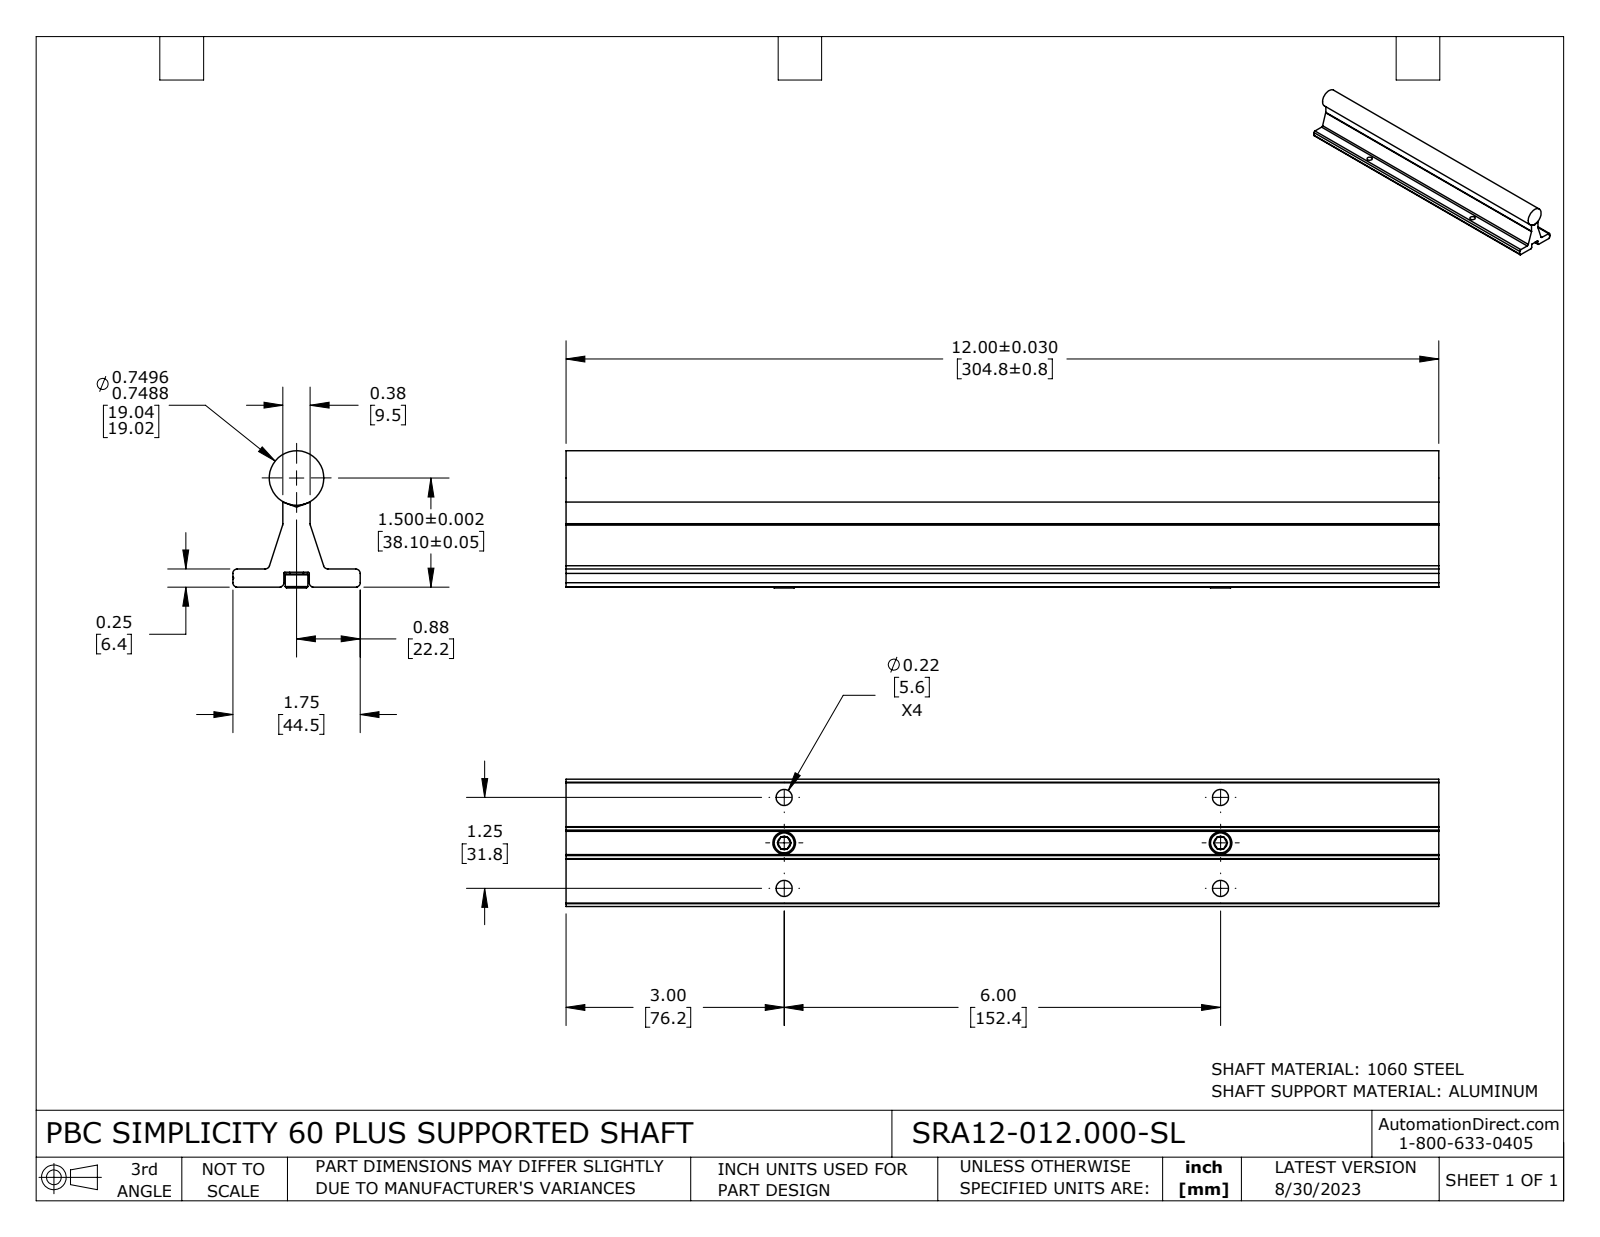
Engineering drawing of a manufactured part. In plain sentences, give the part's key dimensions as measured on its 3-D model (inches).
The part is named "SRA12-012.000-SL". Its 3-D file was written by "SolidWorks 2021 (CONFIG_CONTROL_DESIGN)". It is 4 solids with 121 faces: 49 planar, 42 cylindrical and 30 other. Overall it measures 12 by 1.885 by 1.75 inches. Its volume is 15.04 cubic inches and its surface area 104.3 square inches. Round holes: 6 of diameter 0.221, 2 of diameter 0.169, 2 of diameter 0.25. Round bosses or shafts: 2 of diameter 0.312, 2 of diameter 0.19, 1 of diameter 0.75. Partial cylindrical surfaces (rounded edges, fillets, slot ends): 6 of radius 0.06, 2 of radius 0.015, 2 of radius 0.062, 2 of radius 0.063. The main face-to-face distances are 0.25, 0.205, 0.045, 0.375, 0.012, 0.363, 0.688, 0.7, 1.05, 1.063. The hole center spacings are 0.625, 6.033, 6, 1.25, 6.129.
